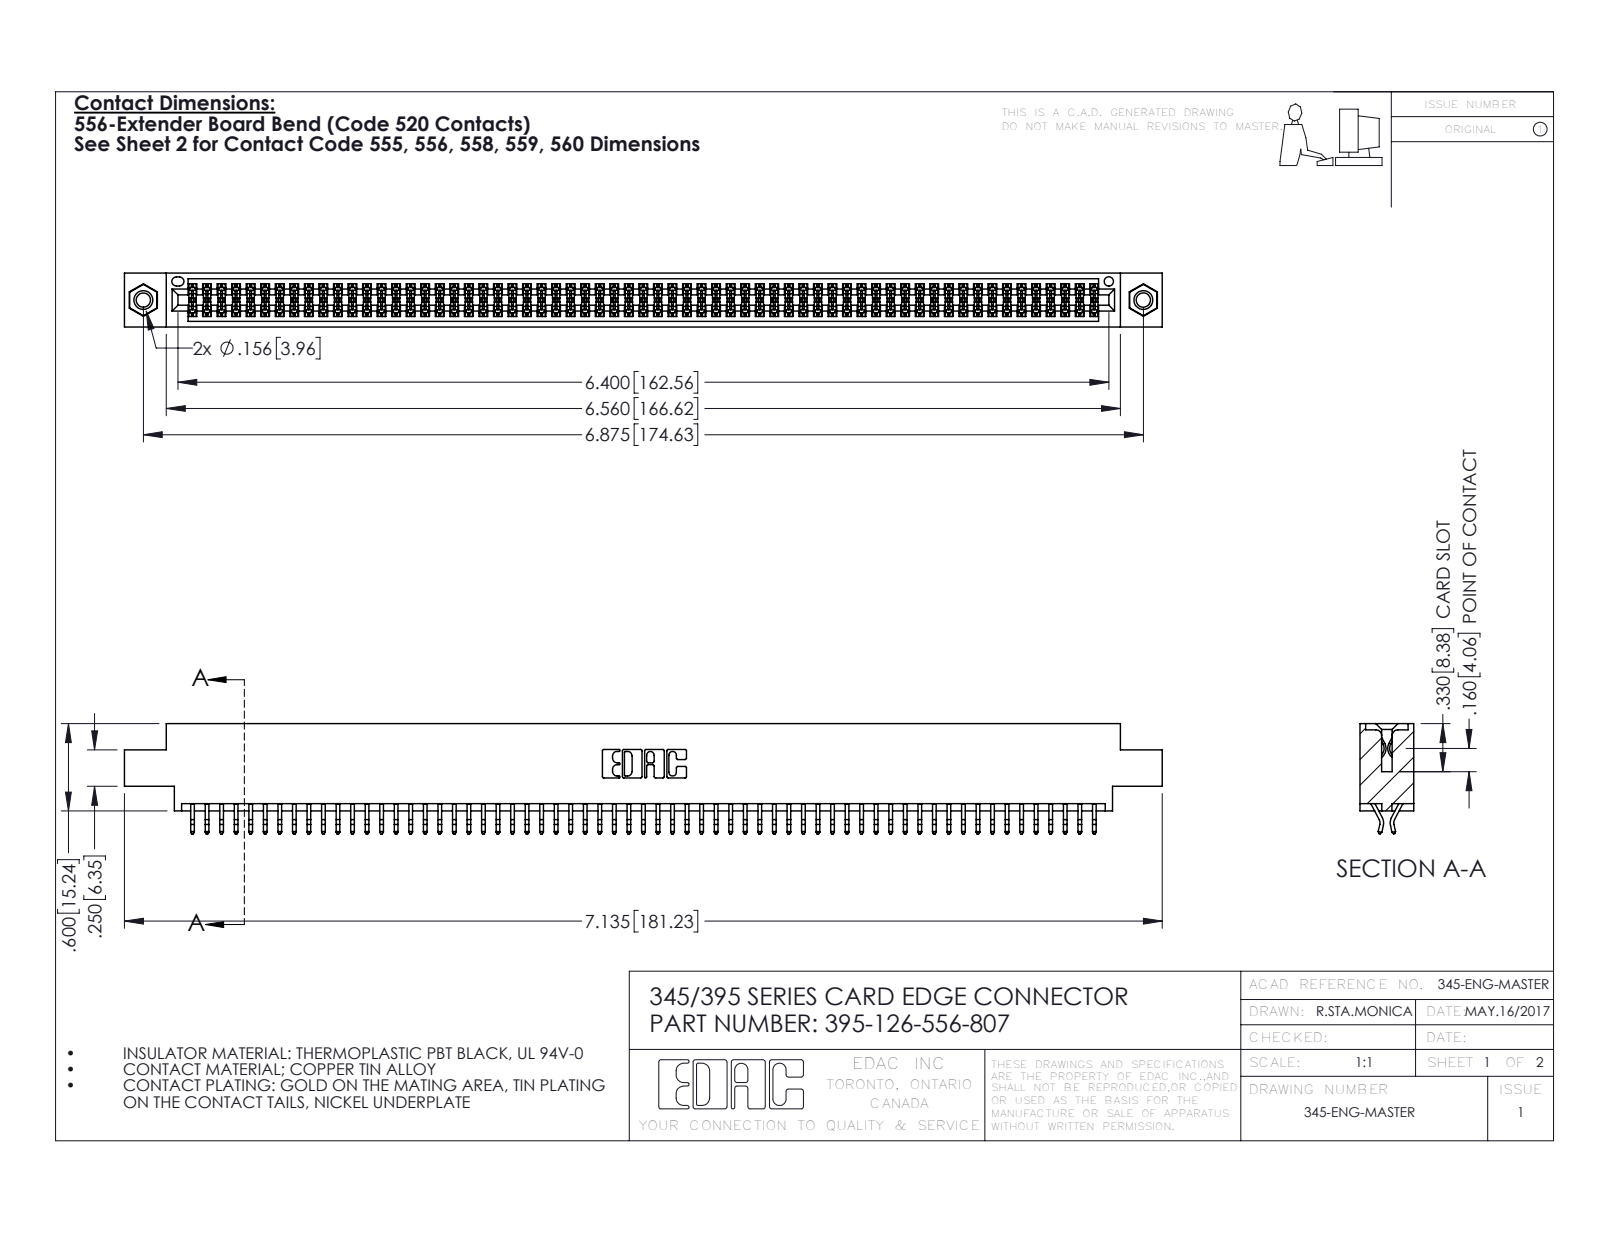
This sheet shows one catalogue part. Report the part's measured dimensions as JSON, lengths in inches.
{"part_name": "345-292-001_556 Tail; 345 Part_0.170 Offset - 0.156 Dia-TI; 345-250-001_345-250-005-103; 395-126-556-807", "step_written_by": "SolidWorks 2016 (CONFIG_CONTROL_DESIGN)", "units": "inches", "bodies": {"solids": 129, "faces": 7246, "planar": 4778, "cylindrical": 2452, "other": 16}, "overall_size": [7.135, 0.757, 0.37], "volume_in3": 1.078, "surface_area_in2": 41.2, "round_holes": [[0.098, 2], [0.125, 2], [0.156, 2], [0.064, 1]], "round_bosses_or_shafts": [[0.155, 2]], "partial_cylinders_radius": [[0.006, 189], [0.01, 22], [0.007, 6], [0.031, 6], [0.026, 3], [0.01, 2], [0.014, 2], [0.019, 2]], "face_to_face_distances": [0.072, 0.298, 0.37, 0.2, 0.025, 0.098, 0.272, 0.225, 0.175, 0.149], "hole_center_spacings": [0.27, 6.639, 6.875]}
